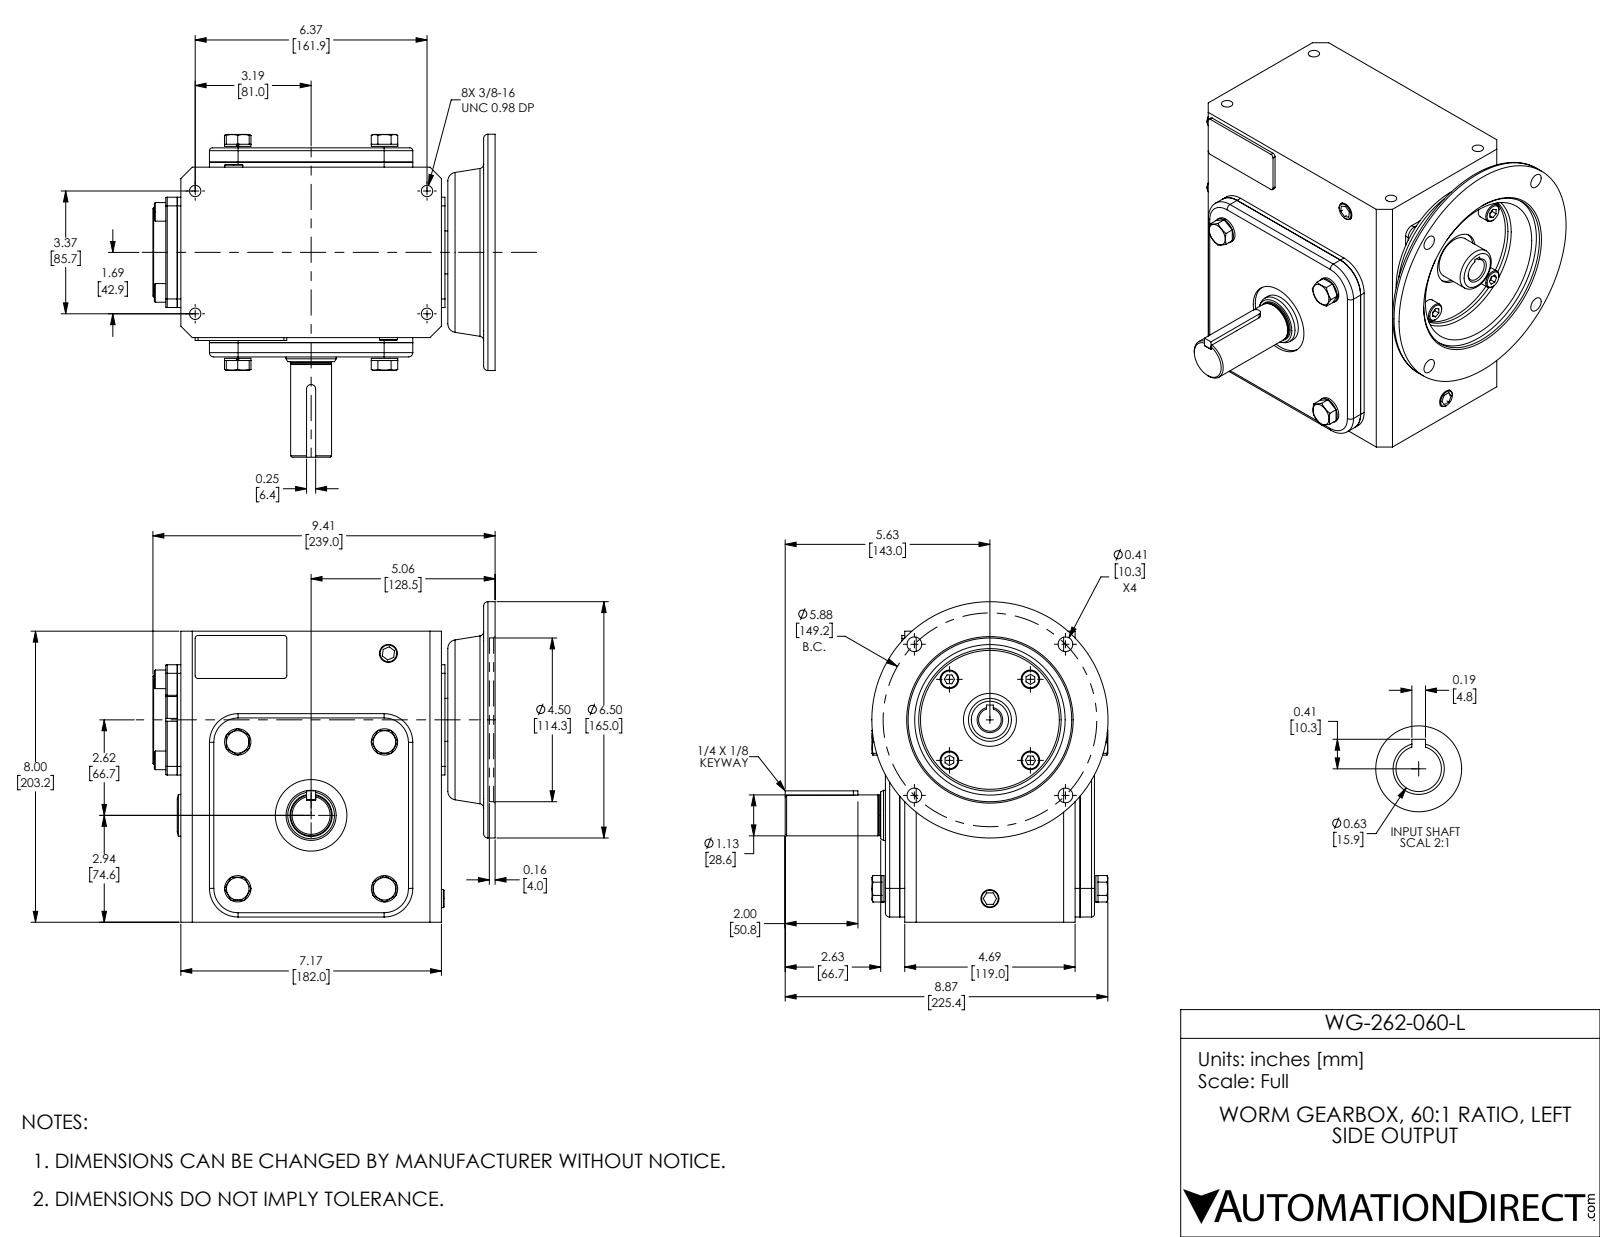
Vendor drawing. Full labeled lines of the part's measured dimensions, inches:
Part name (STEP PRODUCT): WG-262-060-L
STEP written by: SolidWorks 2017 (AUTOMOTIVE_DESIGN)
Units: inches
Bodies: 37 solids, 536 faces (293 planar, 145 cylindrical, 98 other)
Overall size (bounding box): 9.409 × 8.878 × 8.811
Volume: 318.1 in³ · Surface area: 613.7 in²
Round holes (diameter × count): ⌀0.313 ×4, ⌀0.406 ×4, ⌀0.591 ×1, ⌀0.625 ×1, ⌀1.181 ×1, ⌀1.378 ×1, ⌀1.457 ×1, ⌀1.969 ×1, ⌀3.819 ×1, ⌀4.5 ×1
Round bosses / shafts (diameter × count): ⌀0.724 ×4, ⌀0.512 ×4, ⌀6.496 ×1, ⌀2.441 ×1, ⌀2.047 ×1, ⌀1.142 ×1, ⌀1.125 ×1, ⌀1.113 ×1
Partial cylindrical surfaces — rounded edges, fillets, slot ends (radius × count): R0.079 ×12, R0.118 ×4, R0.236 ×4, R0.787 ×4, R0.02 ×2, R0.039 ×2, R0.125 ×1
Main face-to-face distances: 0.394, 4.961, 5.354, 0.531, 5.217, 0.138, 4.823, 8, 0.098, 7.264
Hole centre spacings: 2.937, 4.154, 2.148, 3.375, 5.14, 5.875, 6.375, 7.213
